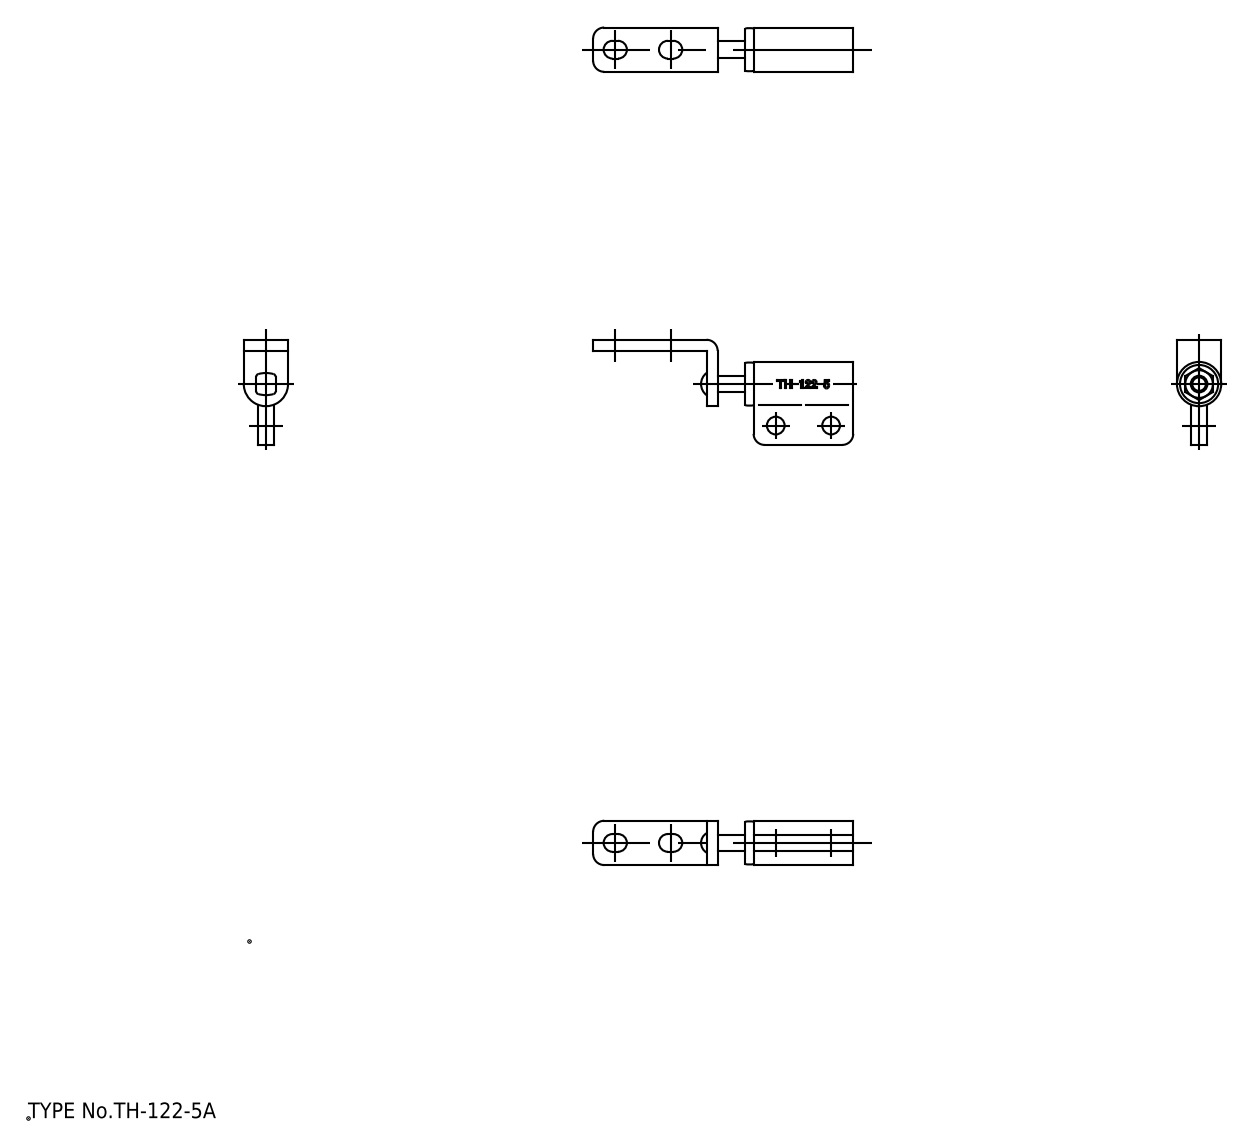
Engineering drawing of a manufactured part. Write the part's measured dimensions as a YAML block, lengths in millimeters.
part_name: "washer; socket; shaft; nut (+2 more)"
step_written_by: "spGate 19.8.4 (****-****-****-****) (AUTOMOTIVE_DESIGN)"
units: millimeters
bodies: {solids: 6, faces: 96, planar: 40, cylindrical: 41, other: 15}
overall_size: [47, 19, 8]
volume: 1462
surface_area: 2953
round_holes:
  - {diameter: 3.2, count: 2}
  - {diameter: 3, count: 1}
  - {diameter: 5.77, count: 1}
  - {diameter: 6.9, count: 1}
round_bosses_or_shafts:
  - {diameter: 8, count: 1}
  - {diameter: 6.3, count: 1}
partial_cylinders:
  - {radius: 2, count: 5}
  - {radius: 0.5, count: 4}
  - {radius: 1.6, count: 4}
  - {radius: 5, count: 2}
  - {radius: 1.52, count: 1}
  - {radius: 2.5, count: 1}
face_to_face_distances: [2, 3, 2.5, 5.5, 6.5, 8.5, 5, 1.5, 17, 8]
hole_center_spacings: [10]
